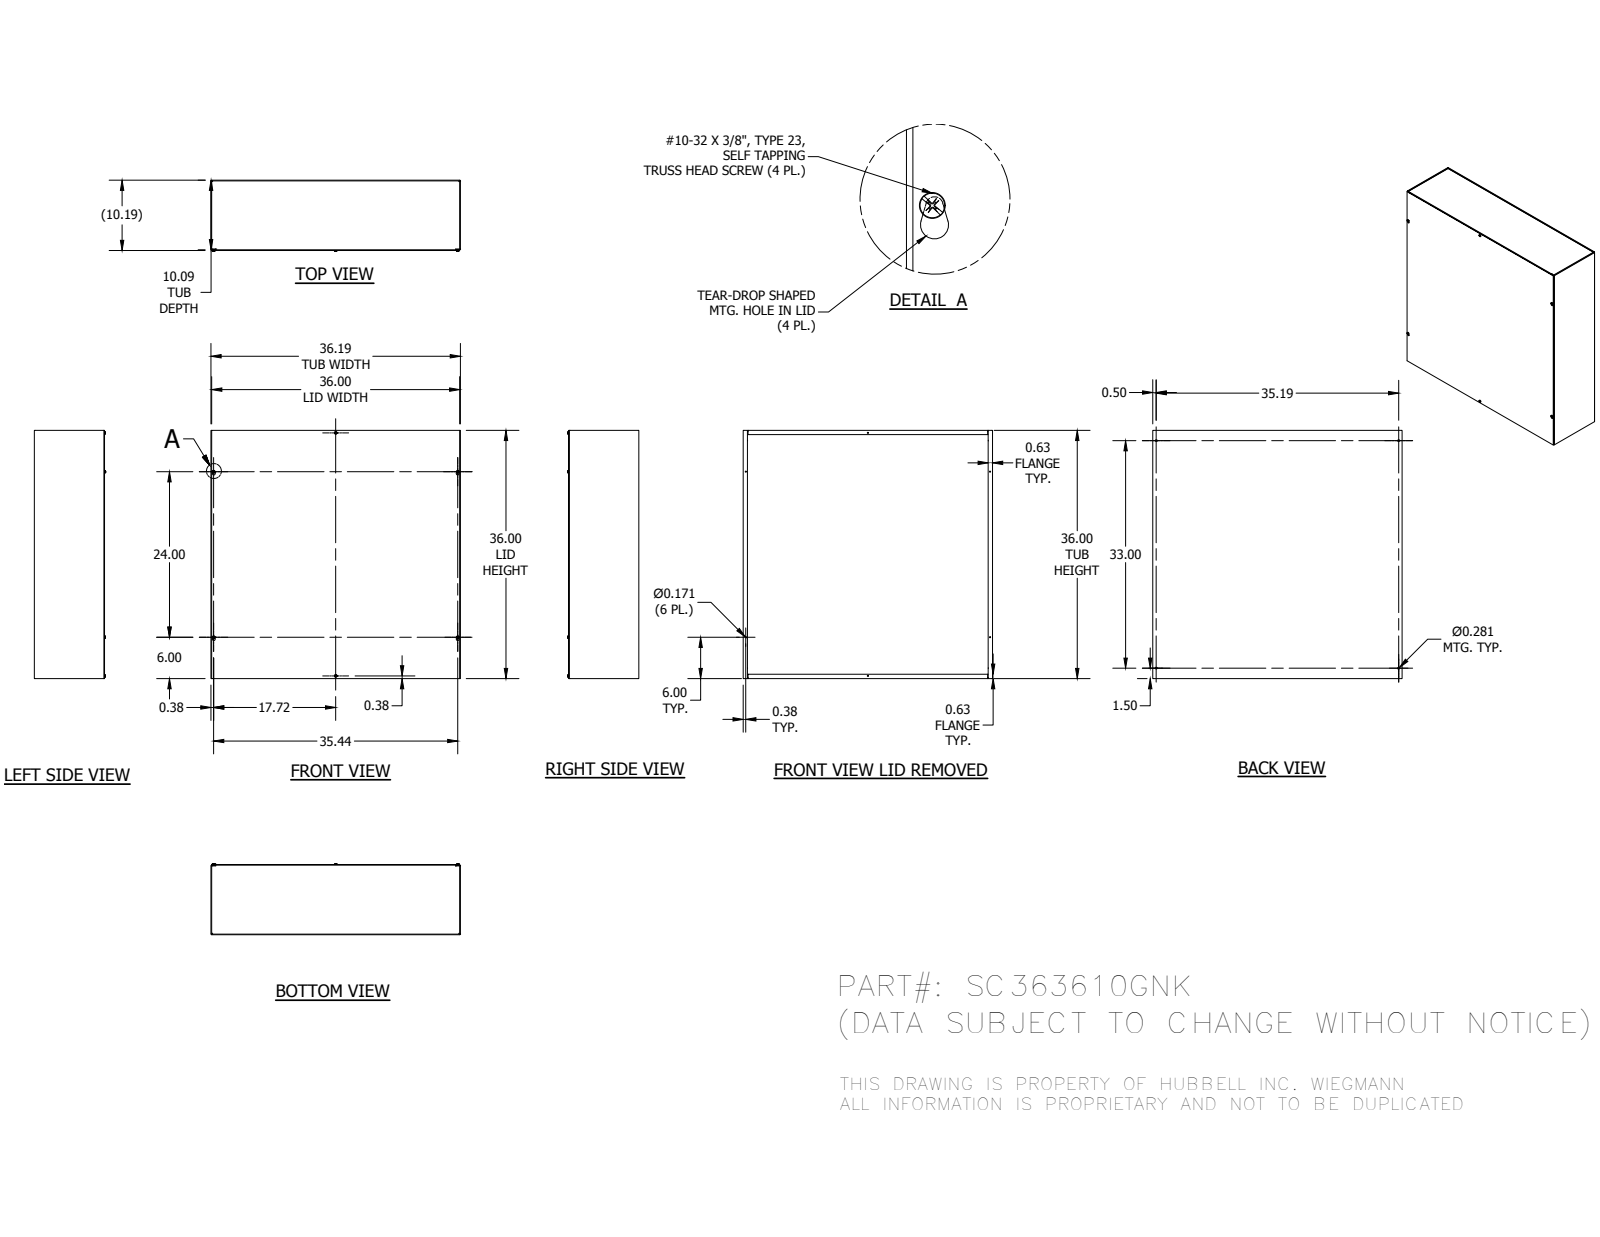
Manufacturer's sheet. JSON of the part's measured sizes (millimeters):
{"part_name": "SC363610GNKBLR; SC3610GNKTB; SC3636GLPA; 37214 (+1 more)", "step_written_by": "Autodesk Inventor 2014 (AUTOMOTIVE_DESIGN)", "units": "millimeters", "bodies": {"solids": 10, "faces": 404, "planar": 232, "cylindrical": 50, "other": 122}, "overall_size": [919.16, 914.4, 262.11], "volume_mm3": 6397000, "surface_area_mm2": 5406000, "round_holes": [[4.34, 6], [7.14, 4], [7.92, 2]], "round_bosses_or_shafts": [[4.83, 6]], "partial_cylinders_radius": [[0.4, 12], [2.78, 12], [3.17, 4], [5.16, 4]], "face_to_face_distances": [2.38, 256.38, 254, 258.76, 914.4, 912.02, 916.78, 909.64, 919.16, 4.76], "hole_center_spacings": [447.79, 114.34, 472.19, 723.91, 876.79, 904.19, 975.19, 1152.62]}
